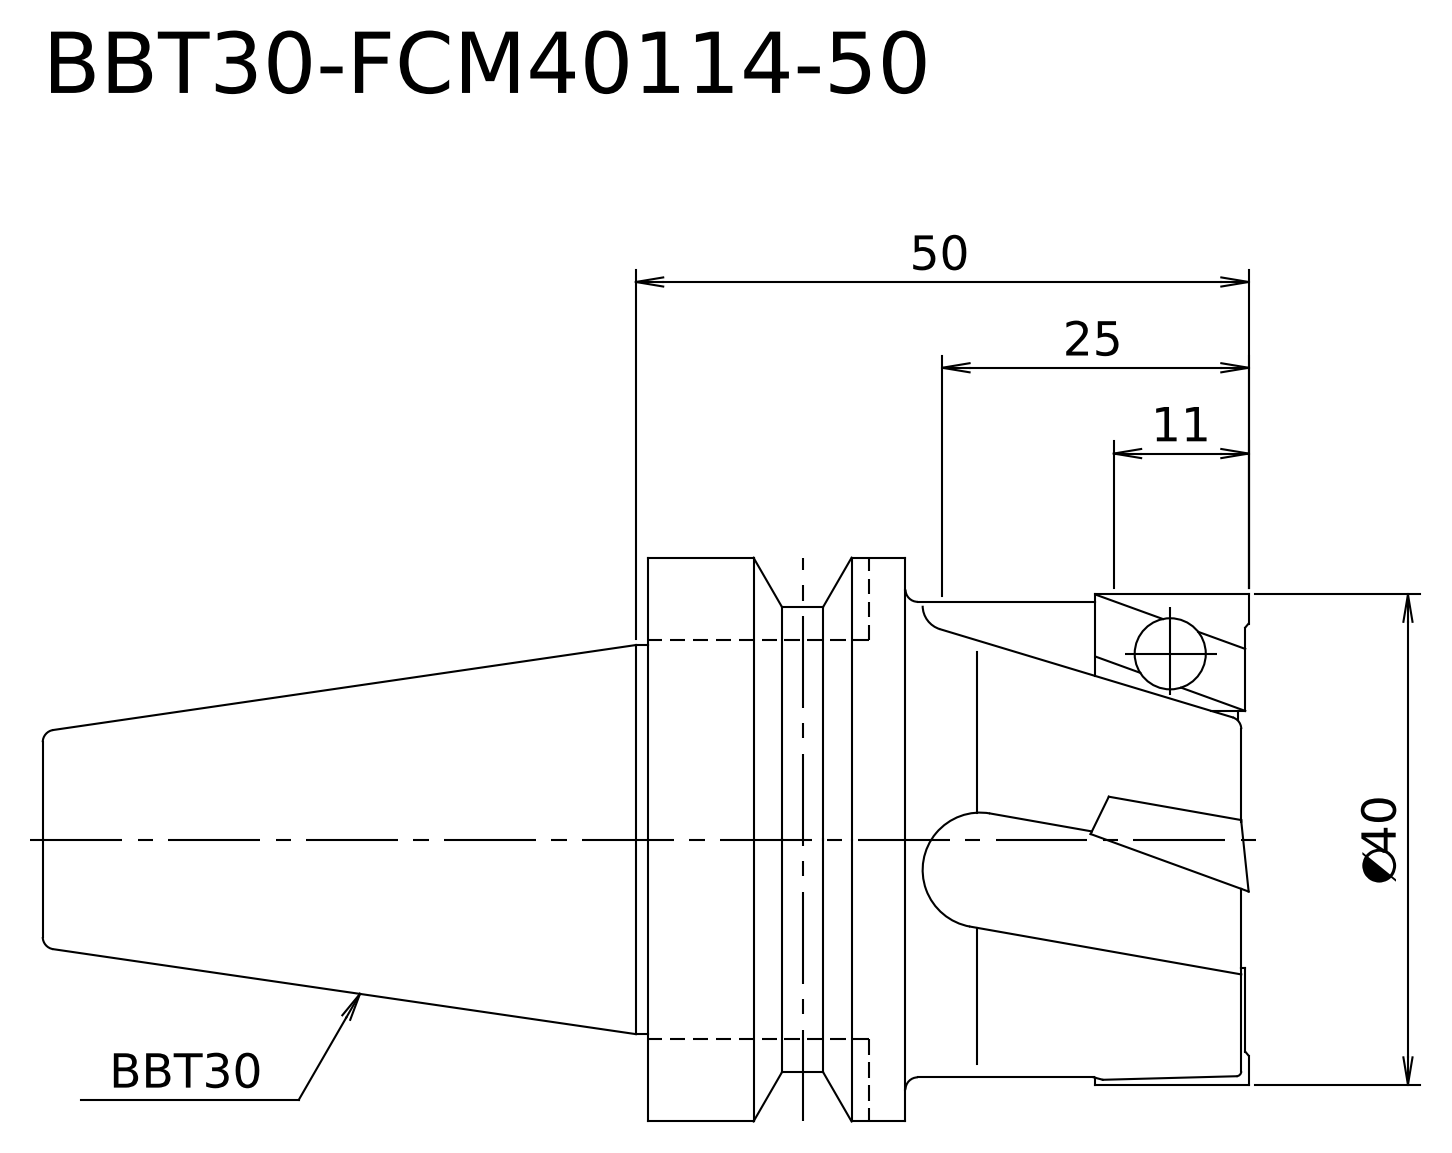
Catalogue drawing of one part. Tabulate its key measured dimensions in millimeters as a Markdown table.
| quantity | value |
| --- | --- |
| STEP written by | Kubotek KeyCreator V8.5.1 (14335) (CONFIG_CONTROL_DESIGN) |
| units | millimeters |
| bodies | 1 solid, 15 faces (4 planar, 6 cylindrical, 5 other) |
| overall size | 98.4 × 46 × 46 |
| volume | 90 503 mm³ |
| surface area | 13 646 mm² |
| round bosses / shafts (diameter × count) | 46 × 1, 40 × 1, 38.8 × 1, 38 × 1, 31.75 × 1 |
| main face-to-face distances | 49, 28, 21, 98.4, 70.4, 49.4 |
